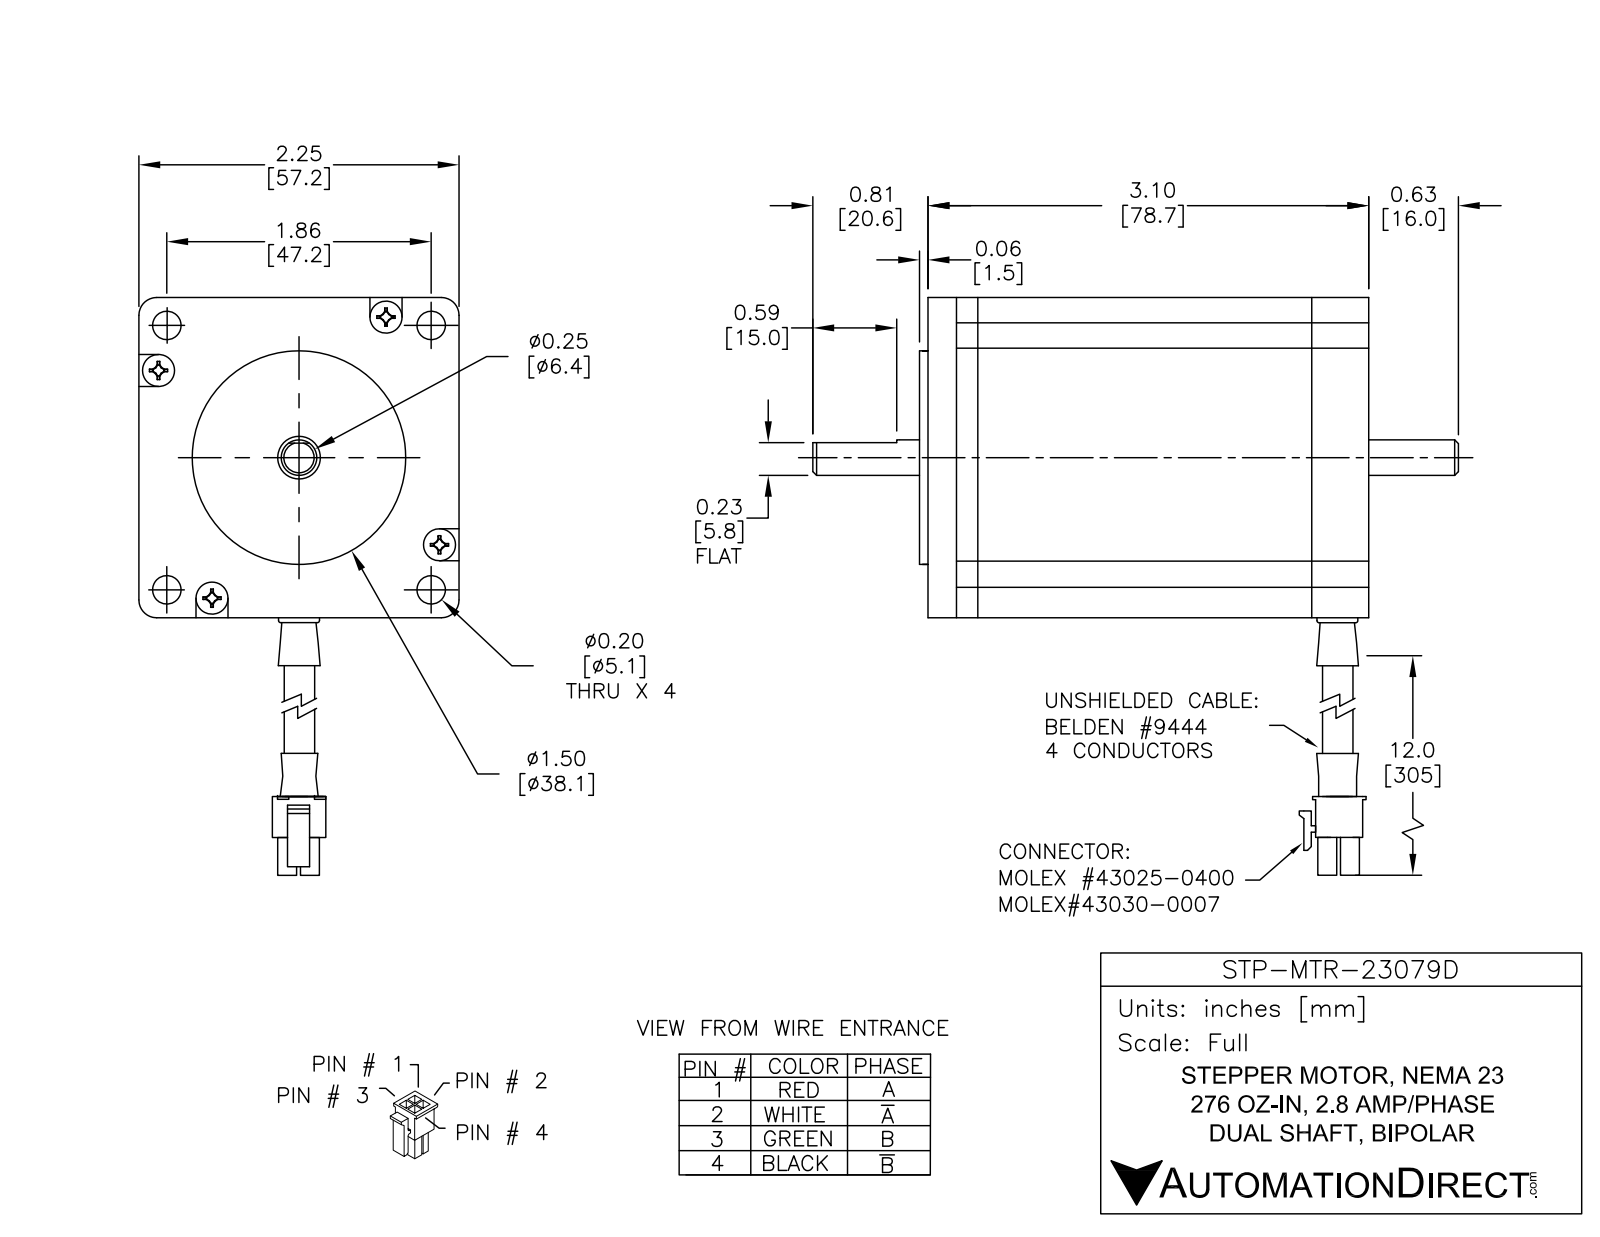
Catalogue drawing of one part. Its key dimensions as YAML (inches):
part_name: "STP-MTR-23079D"
step_written_by: "SolidWorks 2017 (AUTOMOTIVE_DESIGN)"
units: inches
bodies: {solids: 4, faces: 498, planar: 328, cylindrical: 112, other: 58}
overall_size: [14.523, 4.422, 2.207]
volume: 12.93
surface_area: 62.17
round_holes:
  - {diameter: 0.097, count: 4}
  - {diameter: 0.2, count: 4}
  - {diameter: 0.085, count: 2}
  - {diameter: 0.125, count: 2}
  - {diameter: 0.125, count: 2}
  - {diameter: 0.063, count: 1}
  - {diameter: 0.25, count: 1}
  - {diameter: 0.394, count: 1}
  - {diameter: 0.398, count: 1}
  - {diameter: 0.465, count: 1}
  - {diameter: 1.6, count: 1}
  - {diameter: 2.152, count: 1}
round_bosses_or_shafts:
  - {diameter: 1.7, count: 1}
  - {diameter: 1.5, count: 1}
  - {diameter: 0.29, count: 1}
  - {diameter: 0.25, count: 1}
  - {diameter: 0.217, count: 1}
partial_cylinders:
  - {radius: 0.125, count: 10}
  - {radius: 0.03, count: 4}
  - {radius: 0.129, count: 4}
  - {radius: 0.175, count: 4}
  - {radius: 0.196, count: 4}
  - {radius: 0.013, count: 3}
  - {radius: 0.059, count: 2}
  - {radius: 0.006, count: 1}
face_to_face_distances: [2.207, 0.314, 2.014, 1.7, 1.083, 1.398, 3.098, 1.081, 1.395, 3.095]
hole_center_spacings: [0.316, 0.622, 1.159, 1.181, 1.314, 1.553, 1.649, 1.828]
